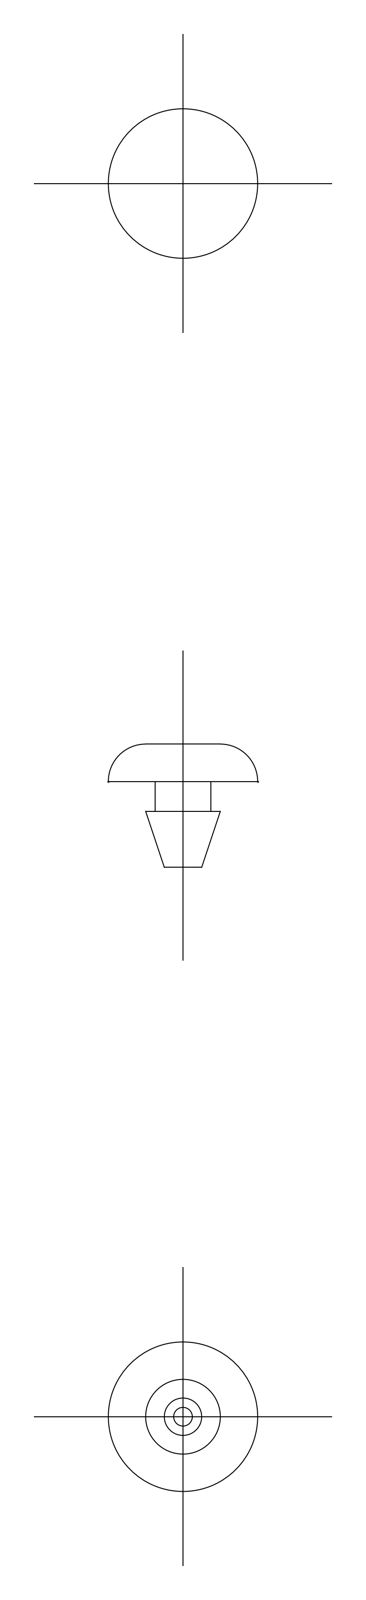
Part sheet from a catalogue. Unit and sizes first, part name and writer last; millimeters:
Units: millimetres
Overall size (bounding box): 8 × 8 × 6.6
Volume: 111 mm³ · Surface area: 188 mm²
Bodies: 1 solid, 13 faces (0 planar, 0 cylindrical, 13 other)
Part name (STEP PRODUCT): cushion
STEP written by: CADfix (AUTOMOTIVE_DESIGN)
